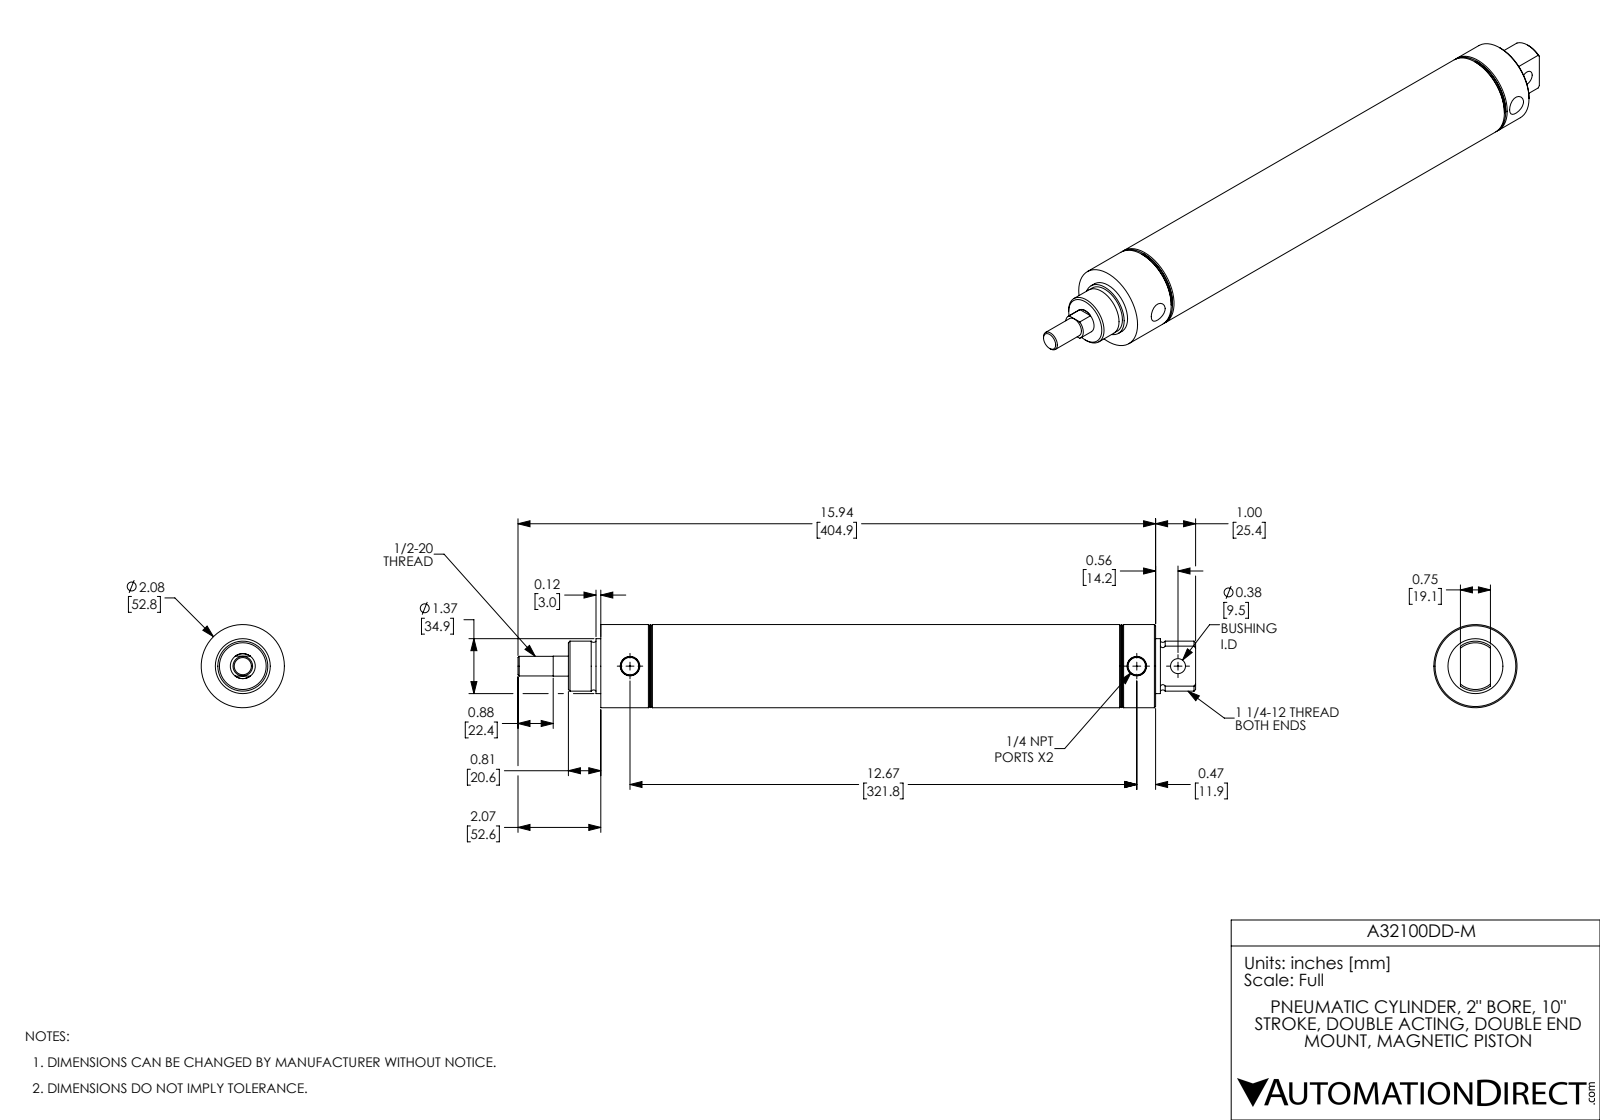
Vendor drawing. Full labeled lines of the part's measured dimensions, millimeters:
Part name (STEP PRODUCT): A32100DD-M; A32100DD-M-Rod; A32100DD-M-MainBody
STEP written by: SolidWorks 2017 (AUTOMOTIVE_DESIGN)
Units: millimetres
Bodies: 2 solids, 88 faces (20 planar, 30 cylindrical, 38 other)
Overall size (bounding box): 430.3 × 52.8 × 52.8
Volume: 337 700 mm³ · Surface area: 142 000 mm²
Round holes (diameter × count): ⌀11.1 ×2, ⌀9.5 ×1, ⌀15.9 ×1, ⌀50.8 ×1
Round bosses / shafts (diameter × count): ⌀52.8 ×1, ⌀34.9 ×1, ⌀31.8 ×1, ⌀12.5 ×1
Main face-to-face distances: 12.7, 266.7, 254, 309.5, 296.8, 42.8, 42.8, 55.5, 309.5, 352.3
Hole centre spacings: 26.2, 321.8, 348
